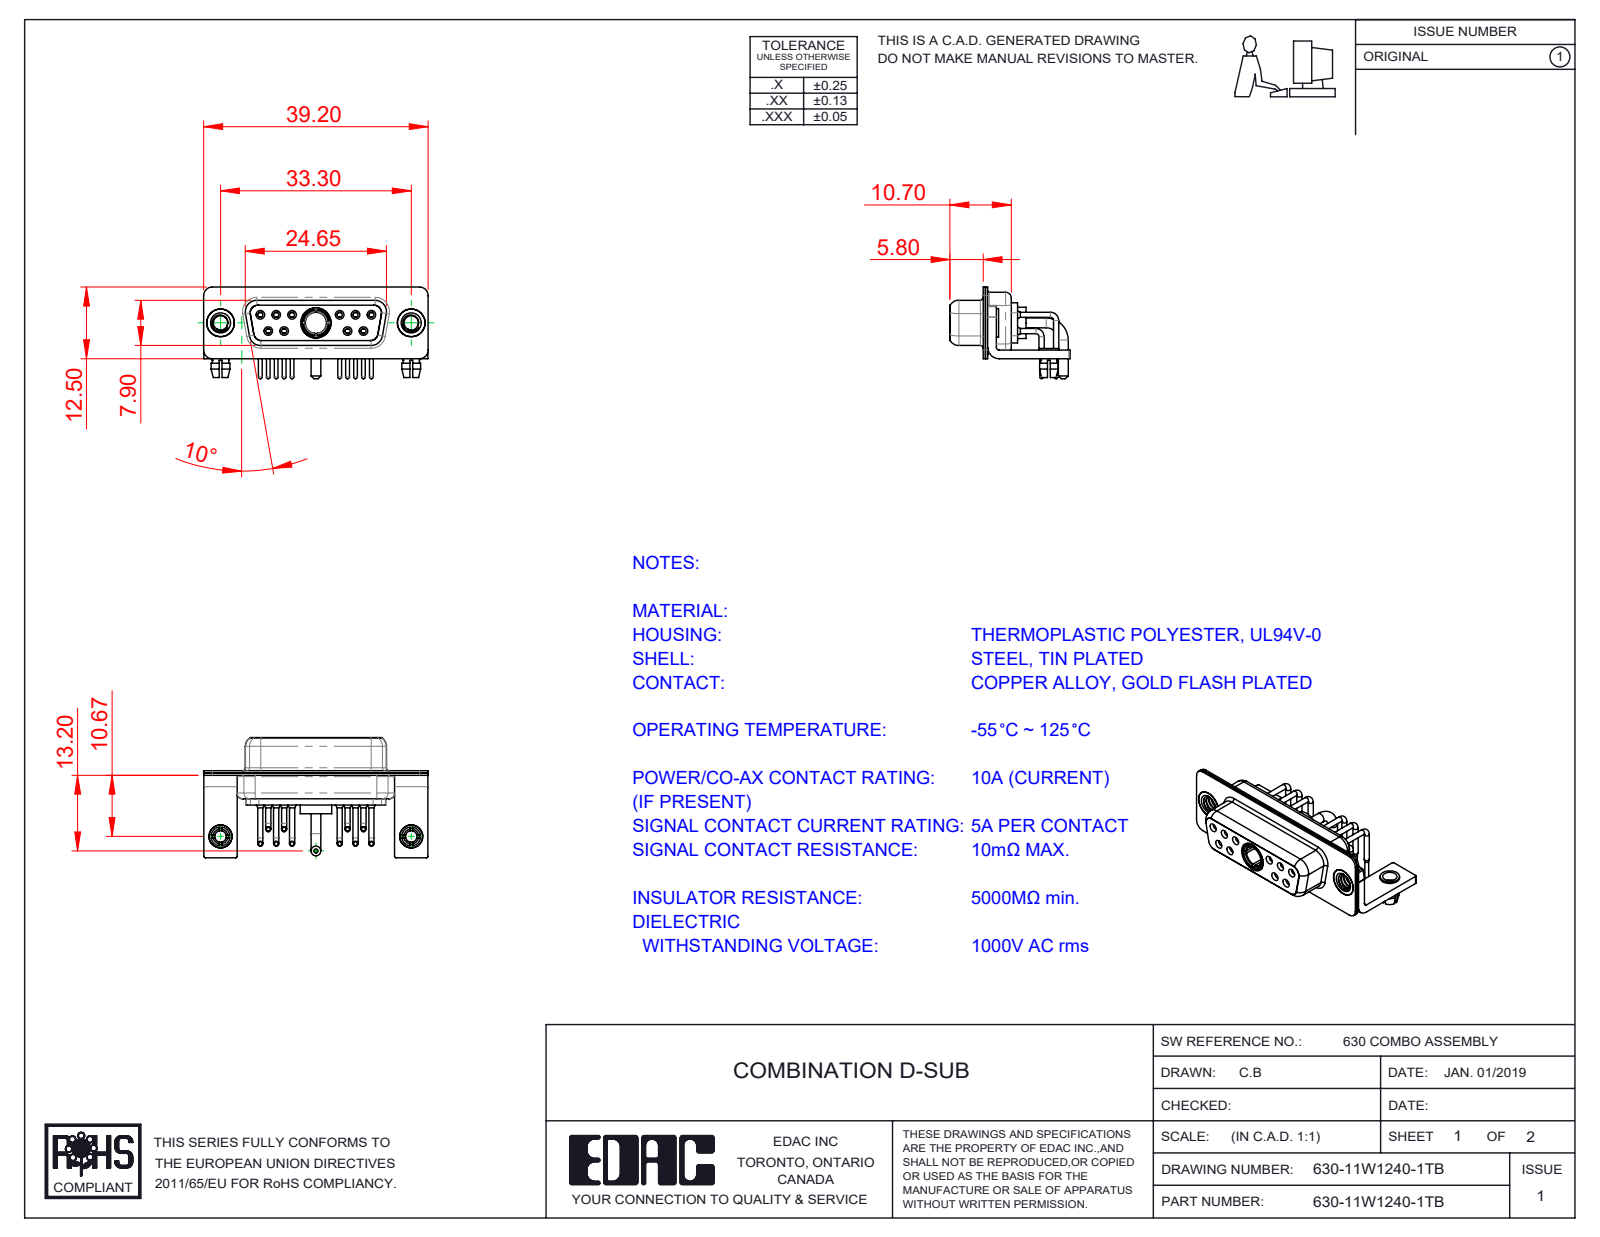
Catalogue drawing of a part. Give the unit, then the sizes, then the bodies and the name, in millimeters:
Units: millimetres
Overall size (bounding box): 39.2 × 21 × 16
Round holes (diameter × count): ⌀2 ×12, ⌀0.9 ×10, ⌀1.1 ×10, ⌀1.5 ×10, ⌀1.7 ×6, ⌀1.6 ×4, ⌀2.5 ×4, ⌀4.85 ×3, ⌀3.2 ×2, ⌀4 ×2, ⌀4.05 ×2, ⌀3.7 ×1
Round bosses / shafts (diameter × count): ⌀0.9 ×10, ⌀0.65 ×10, ⌀1.6 ×6, ⌀5 ×2, ⌀4.95 ×2, ⌀4.8 ×2, ⌀4 ×2, ⌀3.4 ×2
Partial cylindrical surfaces — rounded edges, fillets, slot ends (radius × count): R0.25 ×16, R1.5 ×16, R2 ×13, R1.35 ×12, R1.6 ×8, R0.5 ×5, R0.6 ×4, R0.65 ×4
Main face-to-face distances: 0.4, 0.8, 0.45, 1.4, 8.45, 1.5, 1.8, 8.9, 6.2, 2.3
Hole centre spacings: 3.16, 2.77, 13.85, 11.08, 16.62, 5.03, 5.04, 5.54
Volume: 2 886 mm³ · Surface area: 7 020 mm²
Bodies: 21 solids, 1017 faces (314 planar, 442 cylindrical, 261 other)
Part name (STEP PRODUCT): 630Combo Board Lock; 630Combo Contact Row 2; 630Combo Housing_11W1; 630Combo Shell Rear_15 Contacts (+6 more)
STEP written by: SolidWorks 2020 (CONFIG_CONTROL_DESIGN)
